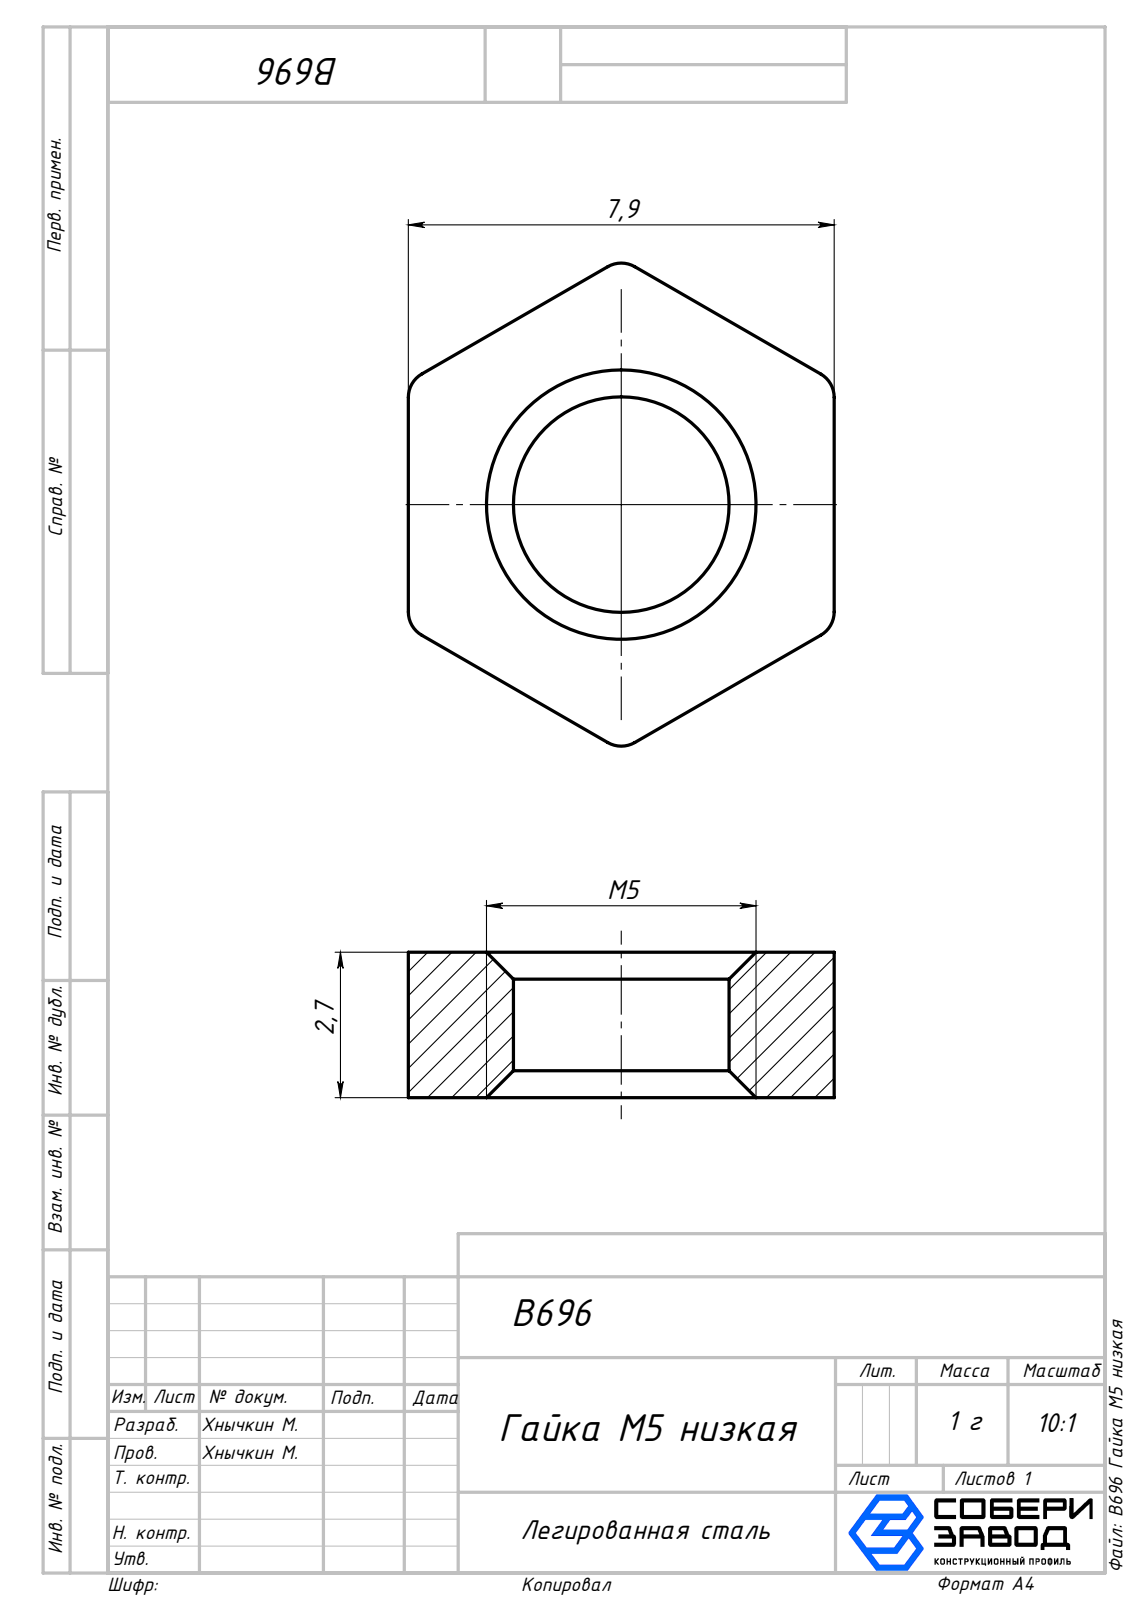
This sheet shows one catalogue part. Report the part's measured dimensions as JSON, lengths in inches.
{"part_name": "B696 Гайка М5 низкая", "step_written_by": "SolidWorks 2025 (AUTOMOTIVE_DESIGN)", "units": "inches", "bodies": {"solids": 1, "faces": 21, "planar": 8, "cylindrical": 9, "other": 4}, "overall_size": [0.353, 0.311, 0.106], "volume_in3": 0.007, "surface_area_in2": 0.284, "round_holes": [[0.157, 1]], "partial_cylinders_radius": [[0.02, 6]], "face_to_face_distances": [0.106, 0.311]}
